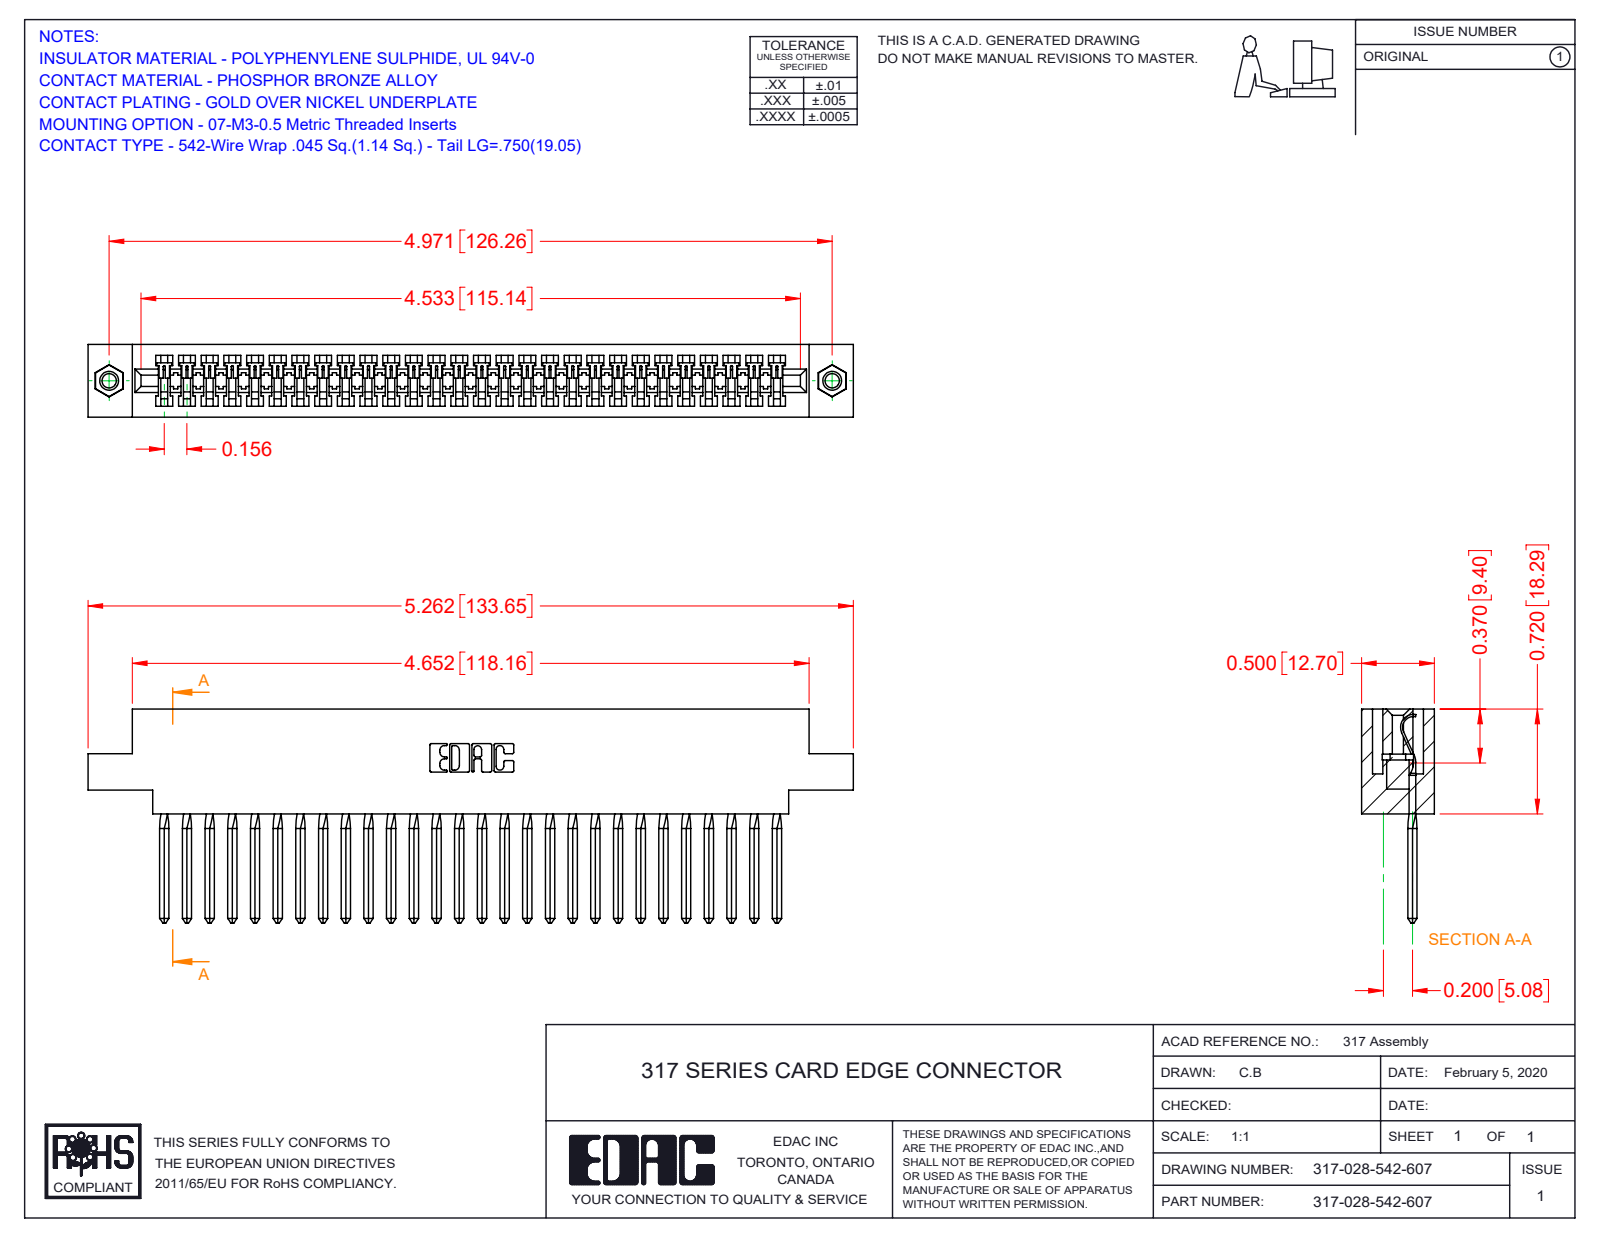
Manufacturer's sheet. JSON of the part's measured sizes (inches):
{"part_name": "345-250-001_345-250-005-103; 317-028-542-607; 317-290-003_542; 317 Part_.156 Dia - TI", "step_written_by": "SolidWorks 2016 (CONFIG_CONTROL_DESIGN)", "units": "inches", "bodies": {"solids": 31, "faces": 2262, "planar": 1882, "cylindrical": 252, "other": 128}, "overall_size": [5.262, 1.47, 0.5], "volume_in3": 1.236, "surface_area_in2": 37.88, "round_holes": [[0.098, 2], [0.125, 2], [0.156, 2]], "round_bosses_or_shafts": [[0.155, 2]], "partial_cylinders_radius": [[0.006, 56], [0.01, 22], [0.007, 6], [0.031, 6], [0.026, 3], [0.074, 1], [0.089, 1], [0.1, 1]], "face_to_face_distances": [0.5, 0.075, 0.425, 0.35, 0.11, 0.136, 0.72, 0.279, 0.211, 0.289], "hole_center_spacings": [4.971]}
